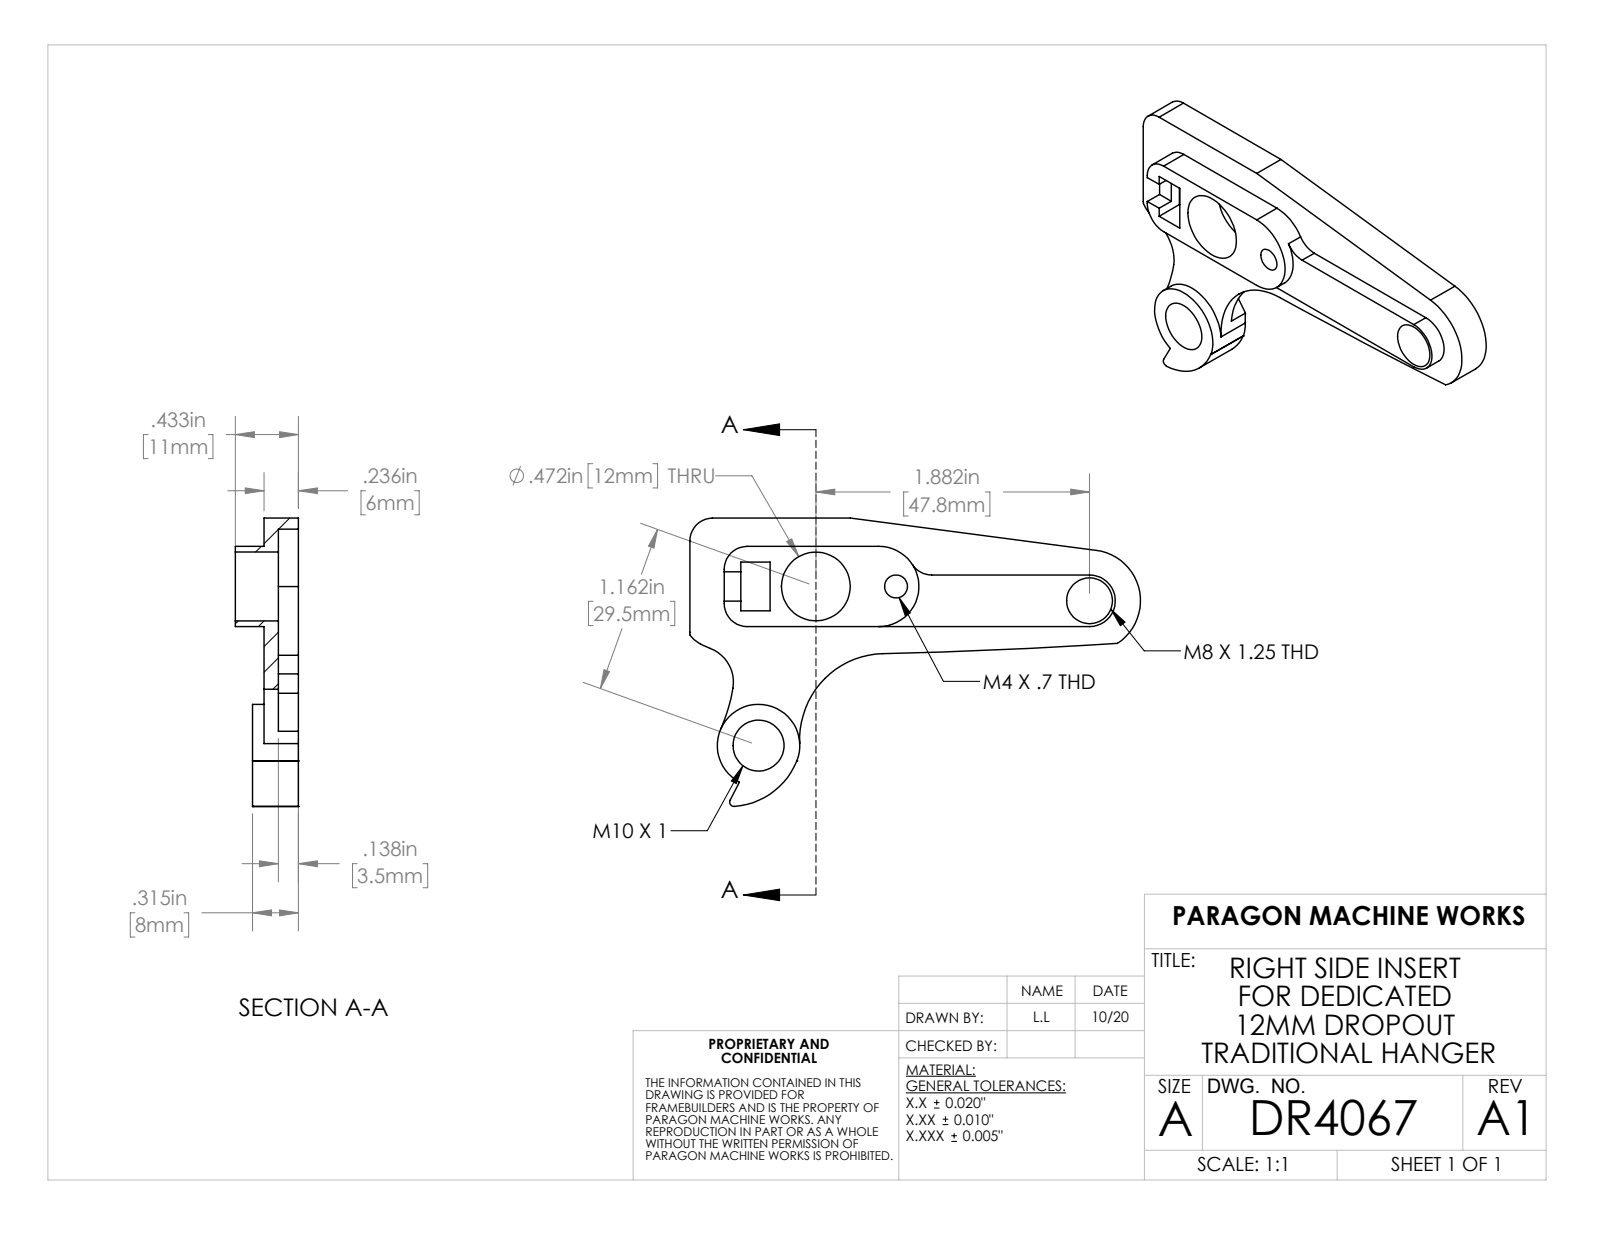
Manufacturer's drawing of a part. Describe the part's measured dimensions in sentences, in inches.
The part is named "DR4067". Its 3-D file was written by "SolidWorks 2021 (AUTOMOTIVE_DESIGN)". It is 1 solid with 64 faces: 28 planar, 36 cylindrical and 0 other. Overall it measures 3.098 by 1.981 by 0.433 inches. Its volume is 0.702 cubic inches and its surface area 10.43 square inches. Round holes: 1 of diameter 0.157, 1 of diameter 0.315, 1 of diameter 0.35, 1 of diameter 0.472. Partial cylindrical surfaces (rounded edges, fillets, slot ends): 5 of radius 0.157, 2 of radius 0.394, 1 of radius 0.03, 1 of radius 0.177, 1 of radius 0.206, 1 of radius 0.25, 1 of radius 0.276, 1 of radius 0.283. The main face-to-face distances are 0.236, 0.079, 0.118, 0.098, 0.138, 0.197, 0.354, 0.295, 0.433, 0.217. The hole center spacings are 0.551, 1.162, 1.334, 1.445, 1.884, 2.483.
